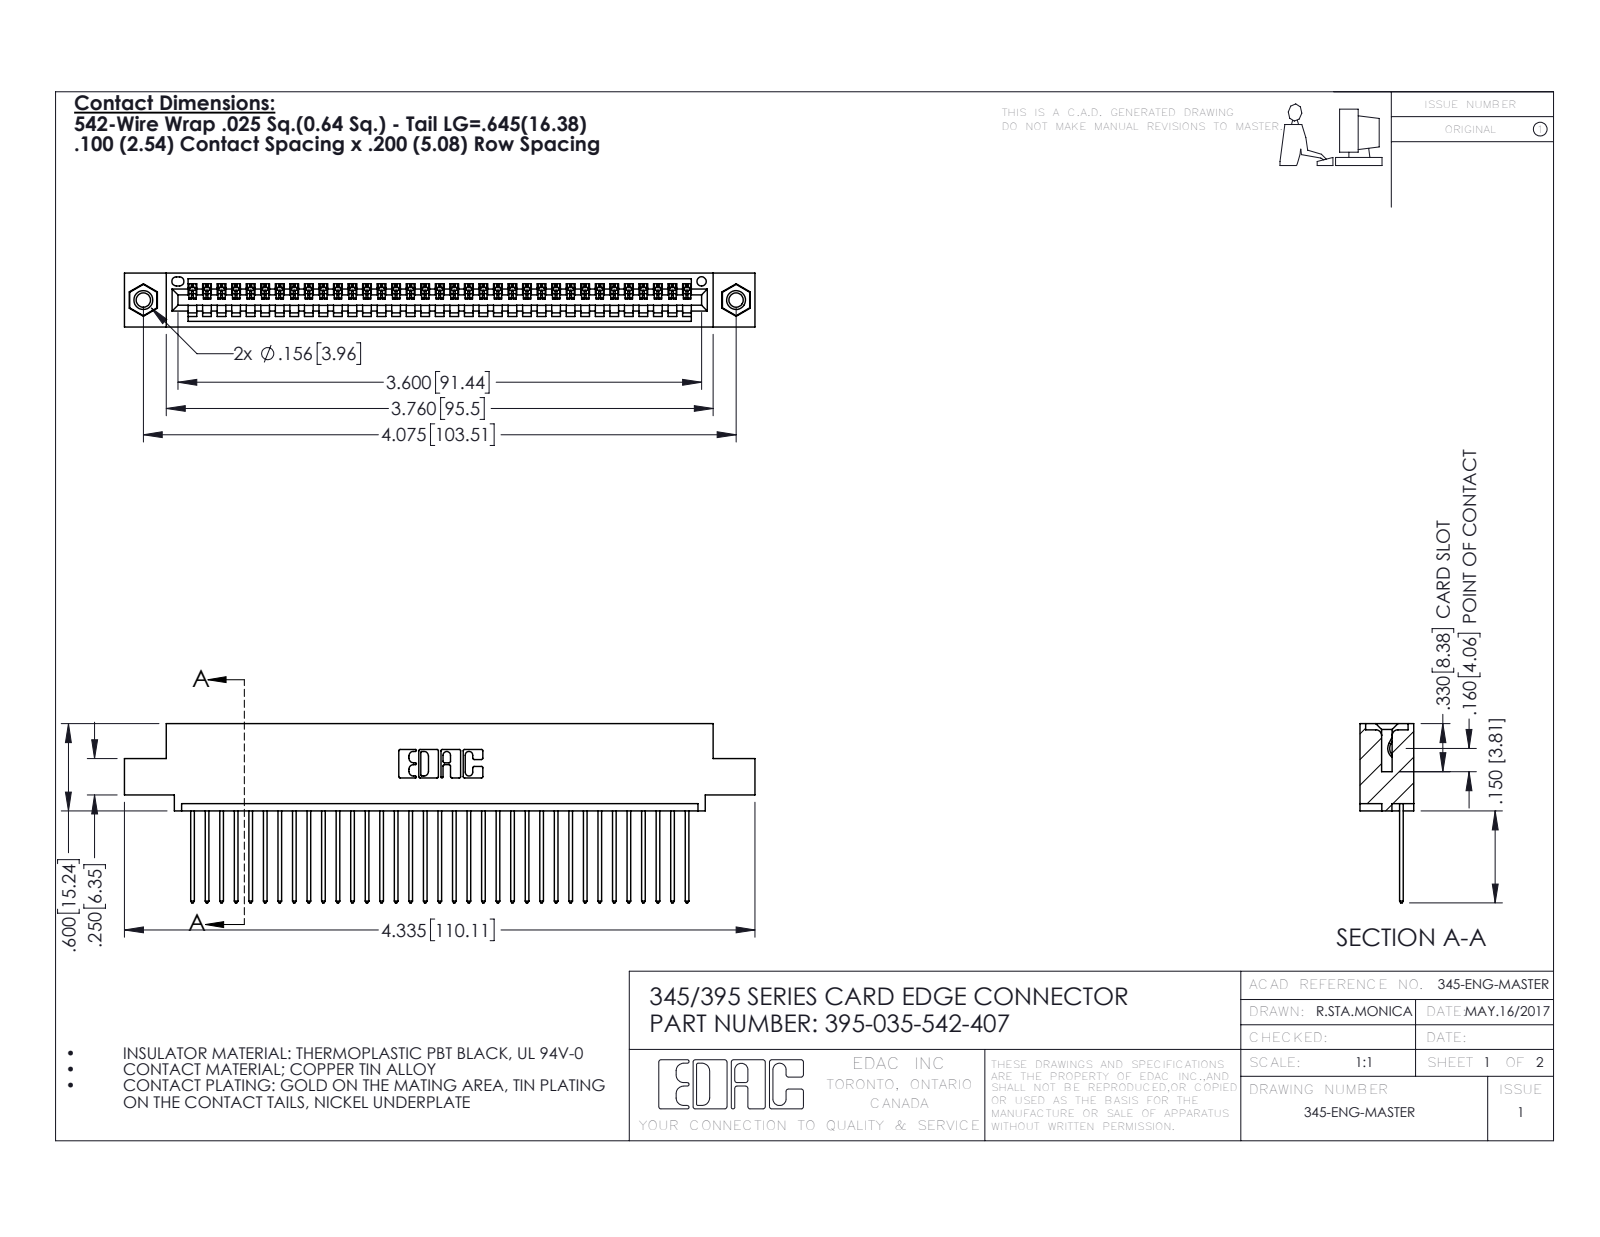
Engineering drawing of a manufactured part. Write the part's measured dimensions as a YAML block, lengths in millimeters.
part_name: "345-292-001_345-293-142; 345 Part_0.110 Offset - 0.156 Dia-TI; 395-035-542-407; 345-250-001_345-250-005-103"
step_written_by: "SolidWorks 2016 (CONFIG_CONTROL_DESIGN)"
units: millimeters
bodies: {solids: 38, faces: 2220, planar: 1516, cylindrical: 688, other: 16}
overall_size: [110.1, 31.3, 9.4]
volume: 10400
surface_area: 14320
round_holes:
  - {diameter: 2.5, count: 2}
  - {diameter: 3.2, count: 2}
  - {diameter: 4, count: 2}
  - {diameter: 1.6, count: 1}
round_bosses_or_shafts:
  - {diameter: 3.9, count: 2}
partial_cylinders:
  - {radius: 0.2, count: 70}
  - {radius: 0.3, count: 70}
  - {radius: 0.3, count: 22}
  - {radius: 0.2, count: 6}
  - {radius: 0.8, count: 6}
  - {radius: 0.7, count: 3}
  - {radius: 0.8, count: 2}
  - {radius: 1, count: 2}
face_to_face_distances: [1.8, 7.6, 9.4, 2.5, 6.9, 0.6, 5.1, 5.7, 3.8, 1.8]
hole_center_spacings: [6.9, 97.5, 103.5]
